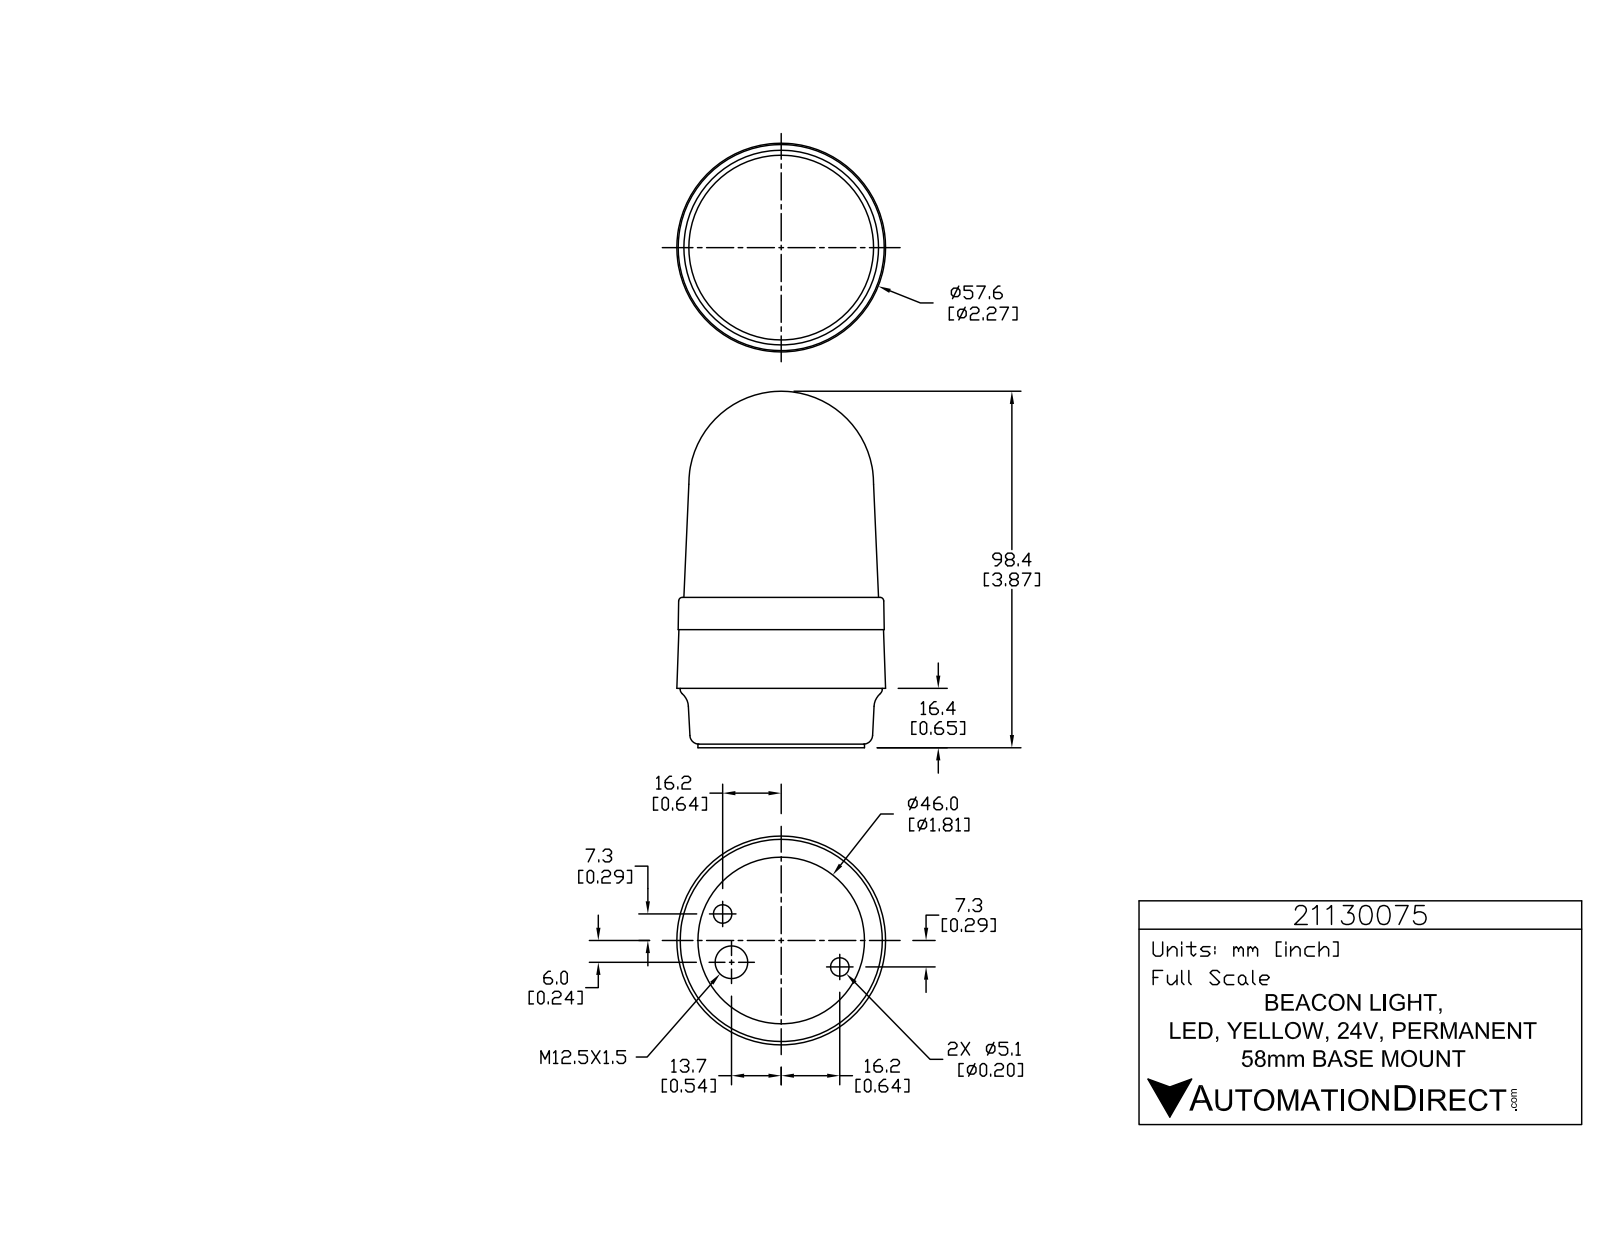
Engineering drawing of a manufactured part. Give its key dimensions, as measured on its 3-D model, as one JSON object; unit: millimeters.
{"part_name": "21130075", "step_written_by": "SolidWorks 2015 (AUTOMOTIVE_DESIGN)", "units": "millimeters", "bodies": {"solids": 1, "faces": 764, "planar": 527, "cylindrical": 145, "other": 92}, "overall_size": [98.4, 57.63, 57.63], "volume_mm3": 199898, "surface_area_mm2": 18922, "round_holes": [[0.99, 3], [5.11, 2], [9, 1]], "round_bosses_or_shafts": [[5.74, 3], [1.43, 3], [55.8, 1], [46, 1]], "partial_cylinders_radius": [[0.2, 6], [0.21, 6], [0.21, 6], [3.32, 6], [0.1, 3], [0.12, 3], [0.19, 3], [0.2, 3]], "face_to_face_distances": [16.4, 1, 15.4, 41.5, 40.5, 25.1, 32.6, 31.6, 16.2, 8.9], "hole_center_spacings": [13.56, 29.94, 35.5]}
